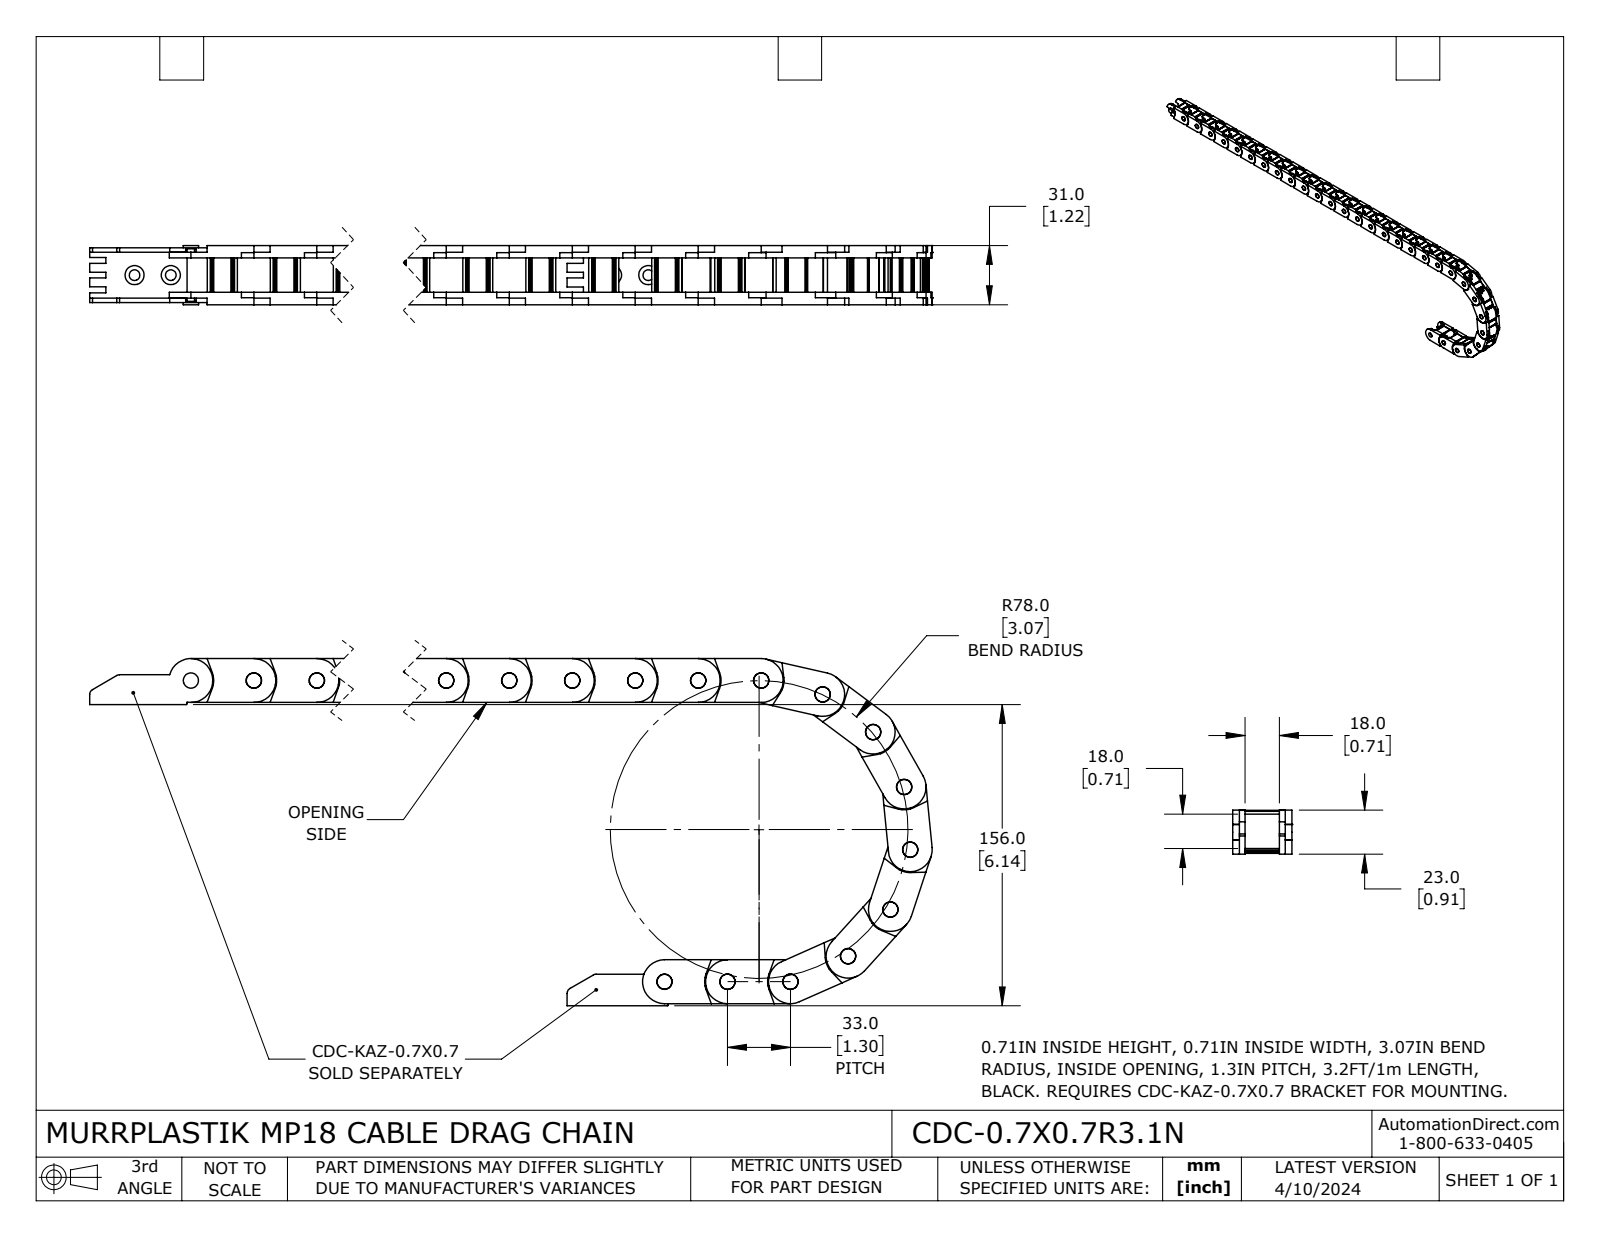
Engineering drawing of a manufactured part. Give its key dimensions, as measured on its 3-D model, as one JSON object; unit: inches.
{"part_name": "CDC-0.7X0.7R3.1N", "step_written_by": "SolidWorks 2023 (CONFIG_CONTROL_DESIGN)", "units": "inches", "bodies": {"solids": 30, "faces": 2790, "planar": 1530, "cylindrical": 1260, "other": 0}, "overall_size": [31.256, 7.115, 1.22], "volume_in3": 18.2, "surface_area_in2": 329.3, "round_holes": [[0.315, 30]], "round_bosses_or_shafts": [[0.315, 1]], "partial_cylinders_radius": [[0.02, 120], [0.059, 120], [0.008, 60], [0.012, 60], [0.453, 31], [0.47, 31], [0.197, 30], [0.215, 30]], "face_to_face_distances": [0.256, 0.965, 1.22, 0.709, 0.138, 1.083, 0.118, 0.827, 0.146, 1.075], "hole_center_spacings": [1.299, 2.598, 3.898, 5.197, 6.496, 7.795, 9.094, 10.394]}
